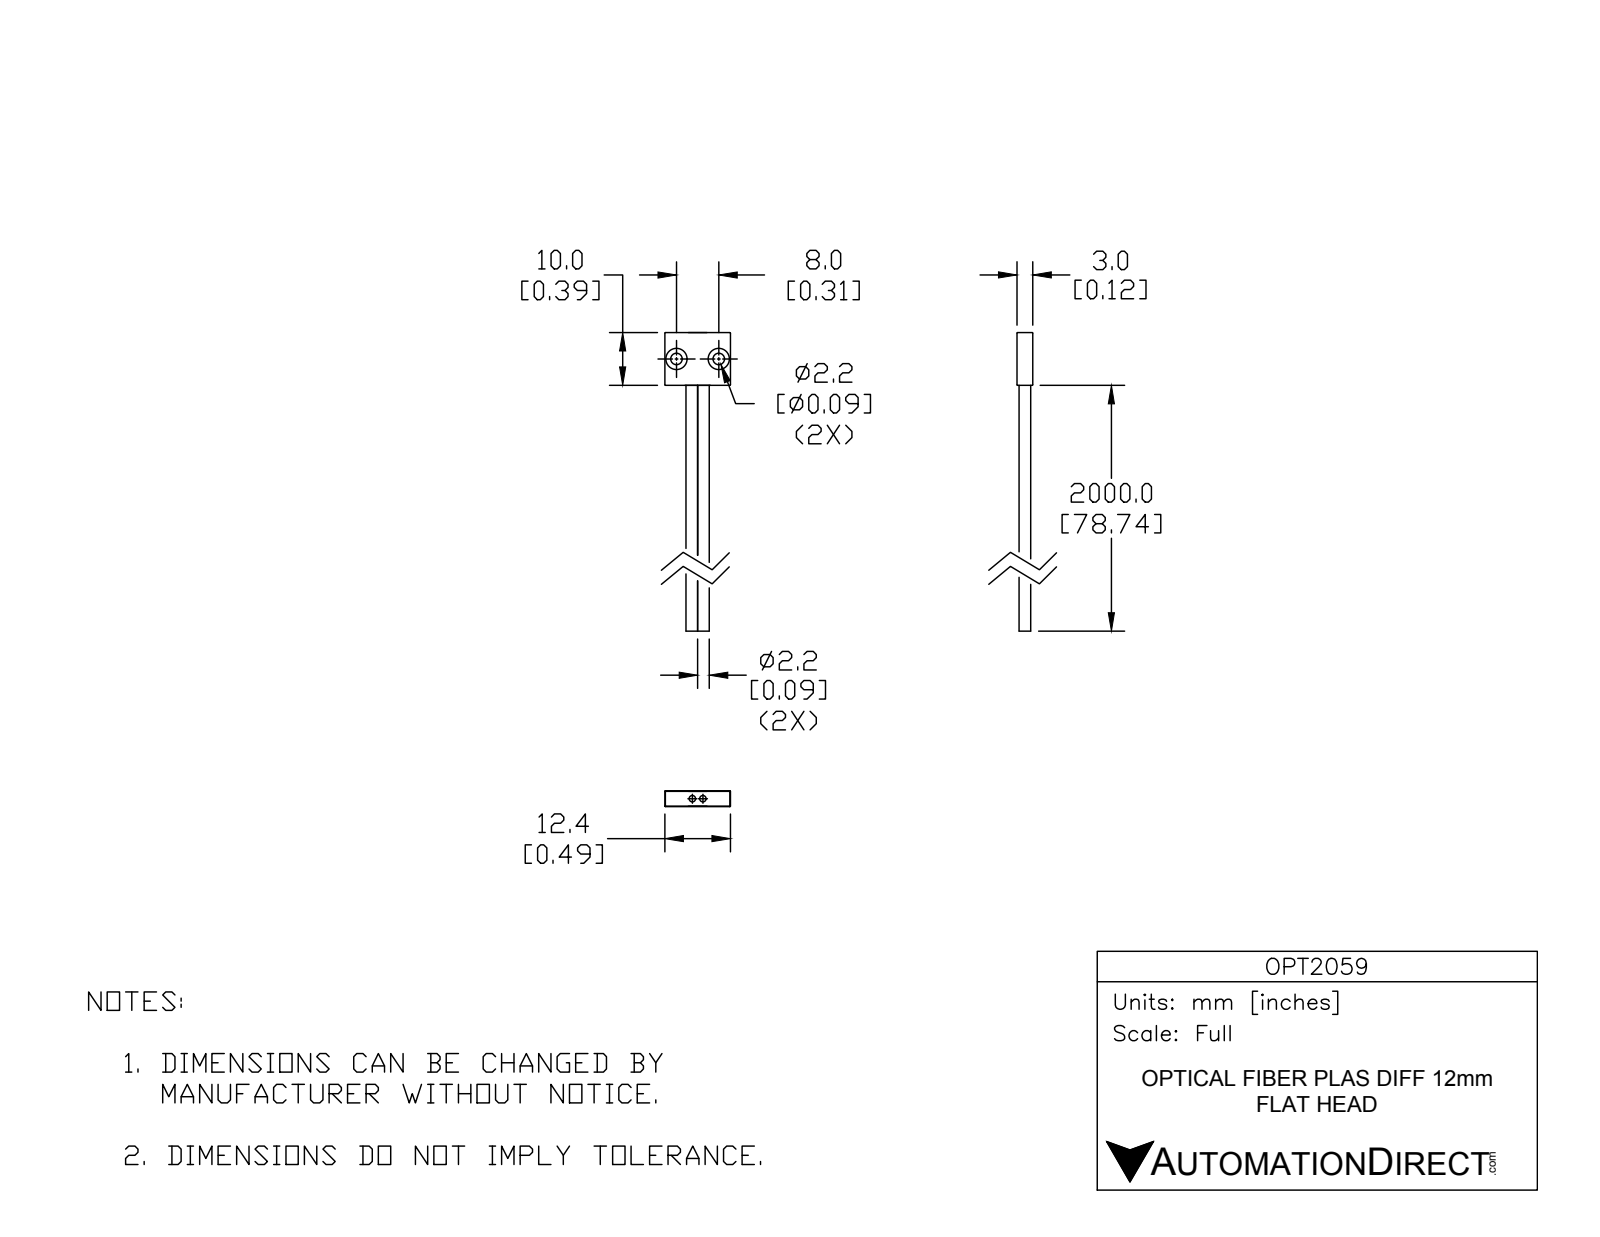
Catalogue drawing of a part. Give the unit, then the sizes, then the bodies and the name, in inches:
Units: inches
Overall size (bounding box): 2.224 × 0.488 × 0.118
Round holes (diameter × count): ⌀0.087 ×2, ⌀0.157 ×2
Round bosses / shafts (diameter × count): ⌀0.087 ×2
Main face-to-face distances: 0.118, 0.488, 0.394, 0.051, 0.067, 1.831, 2.224, 0.356, 0.423, 0.618
Hole centre spacings: 0.315
Volume: 0.041 in³ · Surface area: 1.641 in²
Bodies: 1 solid, 43 faces (29 planar, 14 cylindrical, 0 other)
Part name (STEP PRODUCT): OPT2059
STEP written by: SolidWorks 2014 (AUTOMOTIVE_DESIGN)
